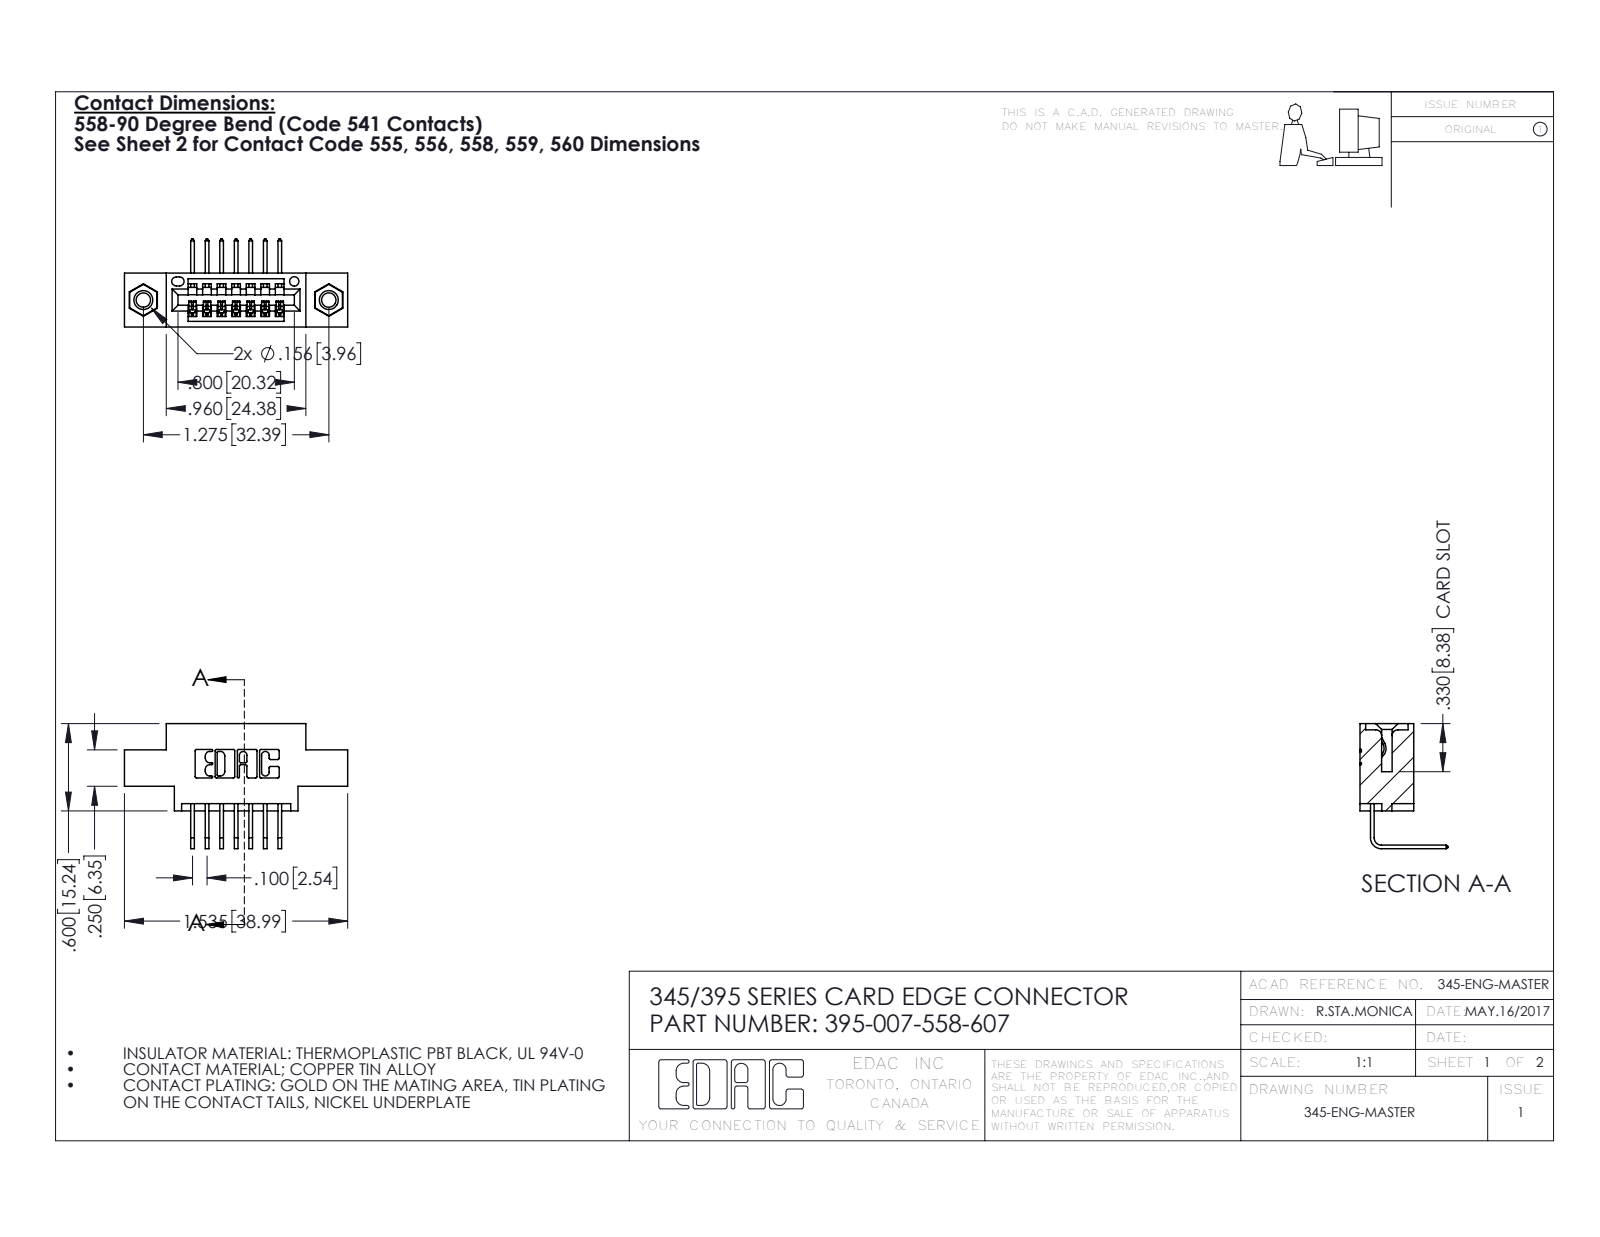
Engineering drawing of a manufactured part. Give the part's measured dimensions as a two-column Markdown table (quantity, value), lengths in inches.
| quantity | value |
| --- | --- |
| part name | 345-292-001_558 Tail - 2; 345-250-001_345-250-005-103; 395-007-558-607; 345 Part_0.170 Offset - 0.156 Dia-TI |
| STEP written by | SolidWorks 2016 (CONFIG_CONTROL_DESIGN) |
| units | inches |
| bodies | 10 solids, 610 faces (410 planar, 184 cylindrical, 16 other) |
| overall size | 1.535 × 0.859 × 0.605 |
| volume | 0.202 in³ |
| surface area | 6.546 in² |
| round holes (diameter × count) | 0.098 × 2, 0.125 × 2, 0.156 × 2, 0.064 × 1 |
| round bosses / shafts (diameter × count) | 0.155 × 2 |
| partial cylindrical surfaces (radius × count) | 0.01 × 22, 0.006 × 14, 0.007 × 6, 0.031 × 6, 0.026 × 3, 0.031 × 2, 0.04 × 2, 0.014 × 1 |
| main face-to-face distances | 0.2, 0.37, 0.1, 0.072, 0.298, 0.3, 0.098, 0.272, 0.025, 0.06 |
| hole center spacings | 0.27, 1.045, 1.275 |
